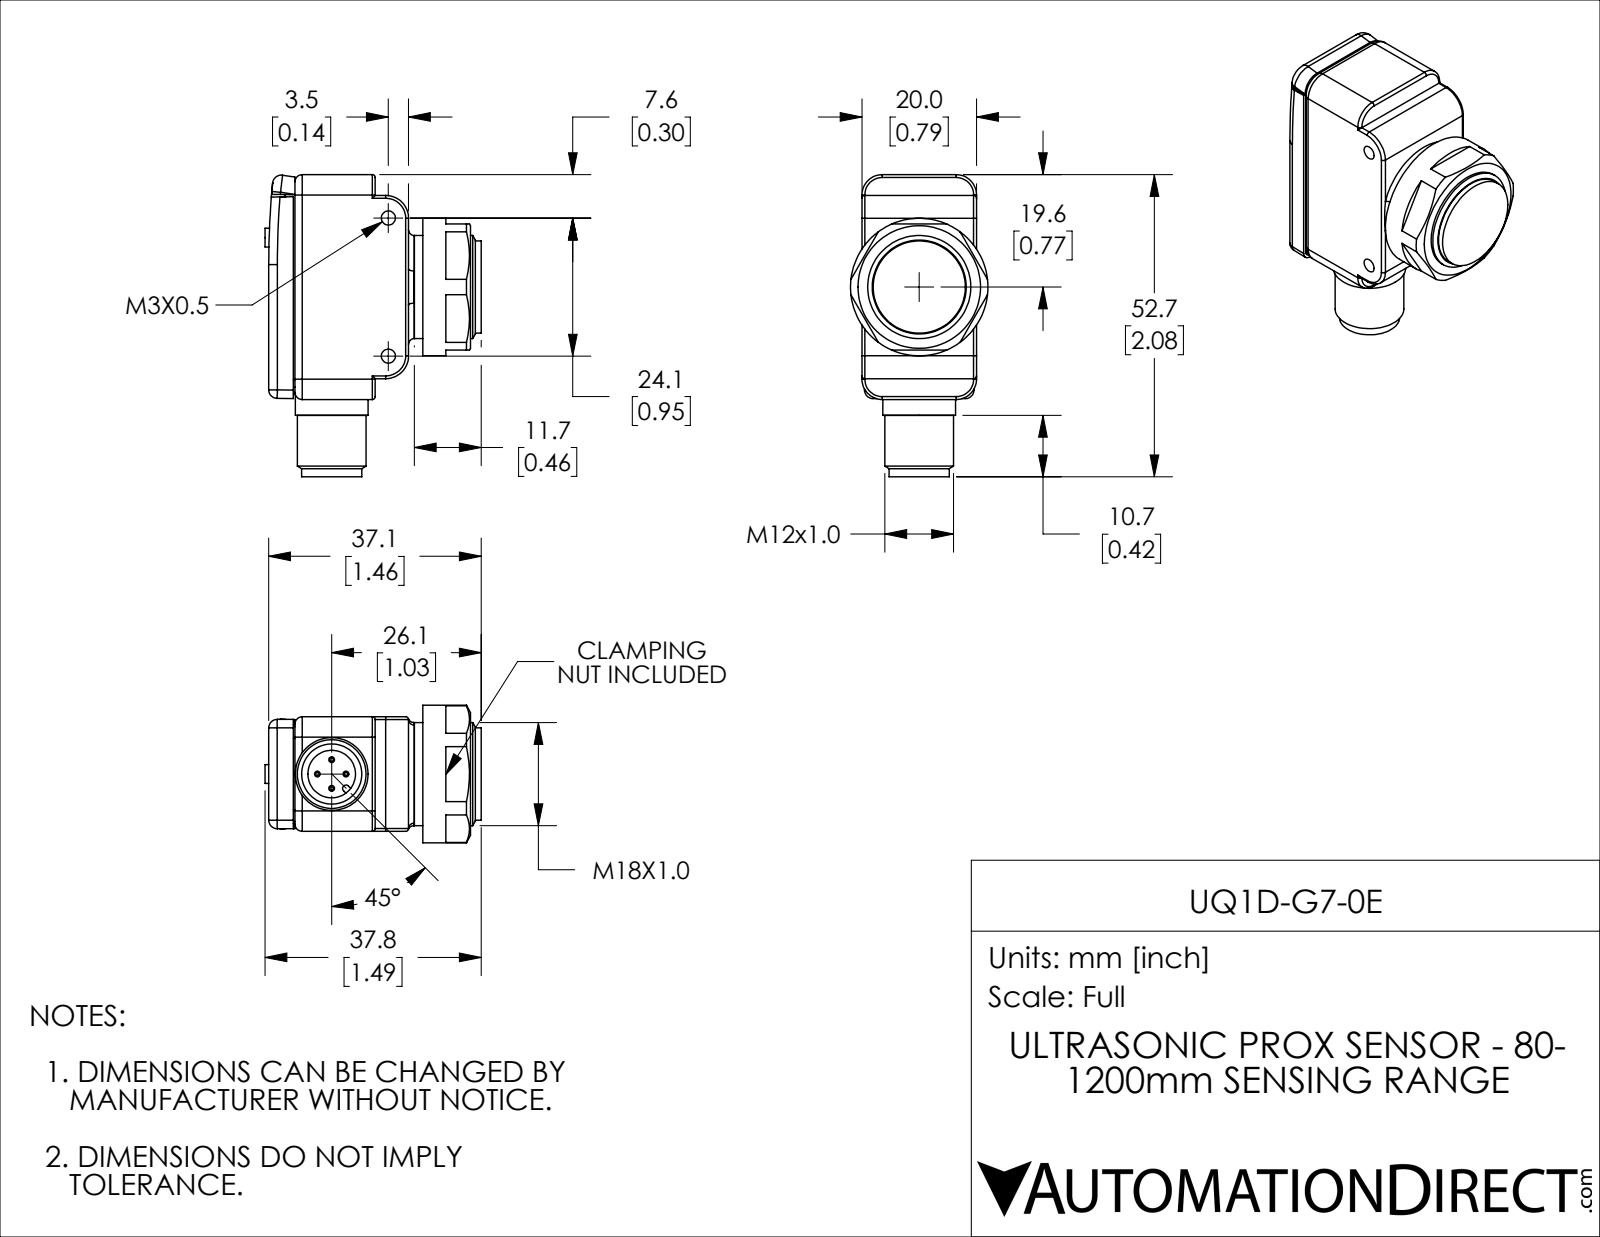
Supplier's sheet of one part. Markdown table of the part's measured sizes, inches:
| quantity | value |
| --- | --- |
| part name | UQ1D-G7-0E |
| STEP written by | SolidWorks 2018 (AUTOMOTIVE_DESIGN) |
| units | inches |
| bodies | 7 solids, 203 faces (81 planar, 72 cylindrical, 50 other) |
| overall size | 2.076 × 1.486 × 0.945 |
| volume | 1.389 in³ |
| surface area | 17.13 in² |
| round holes (diameter × count) | 0.097 × 2, 0.13 × 1, 0.327 × 1 |
| round bosses / shafts (diameter × count) | 0.039 × 4, 0.945 × 1, 0.709 × 1, 0.634 × 1, 0.5 × 1, 0.472 × 1, 0.413 × 1 |
| partial cylindrical surfaces (radius × count) | 0.02 × 10, 0.059 × 6, 0.049 × 4, 0.14 × 4, 0.118 × 2, 0.157 × 2, 5.906 × 2, 0.024 × 1 |
| main face-to-face distances | 0.091, 0.787, 0.911, 0.82, 0.09, 0.181, 1.001, 0.459, 1.46, 1.37 |
| hole center spacings | 0.949 |
